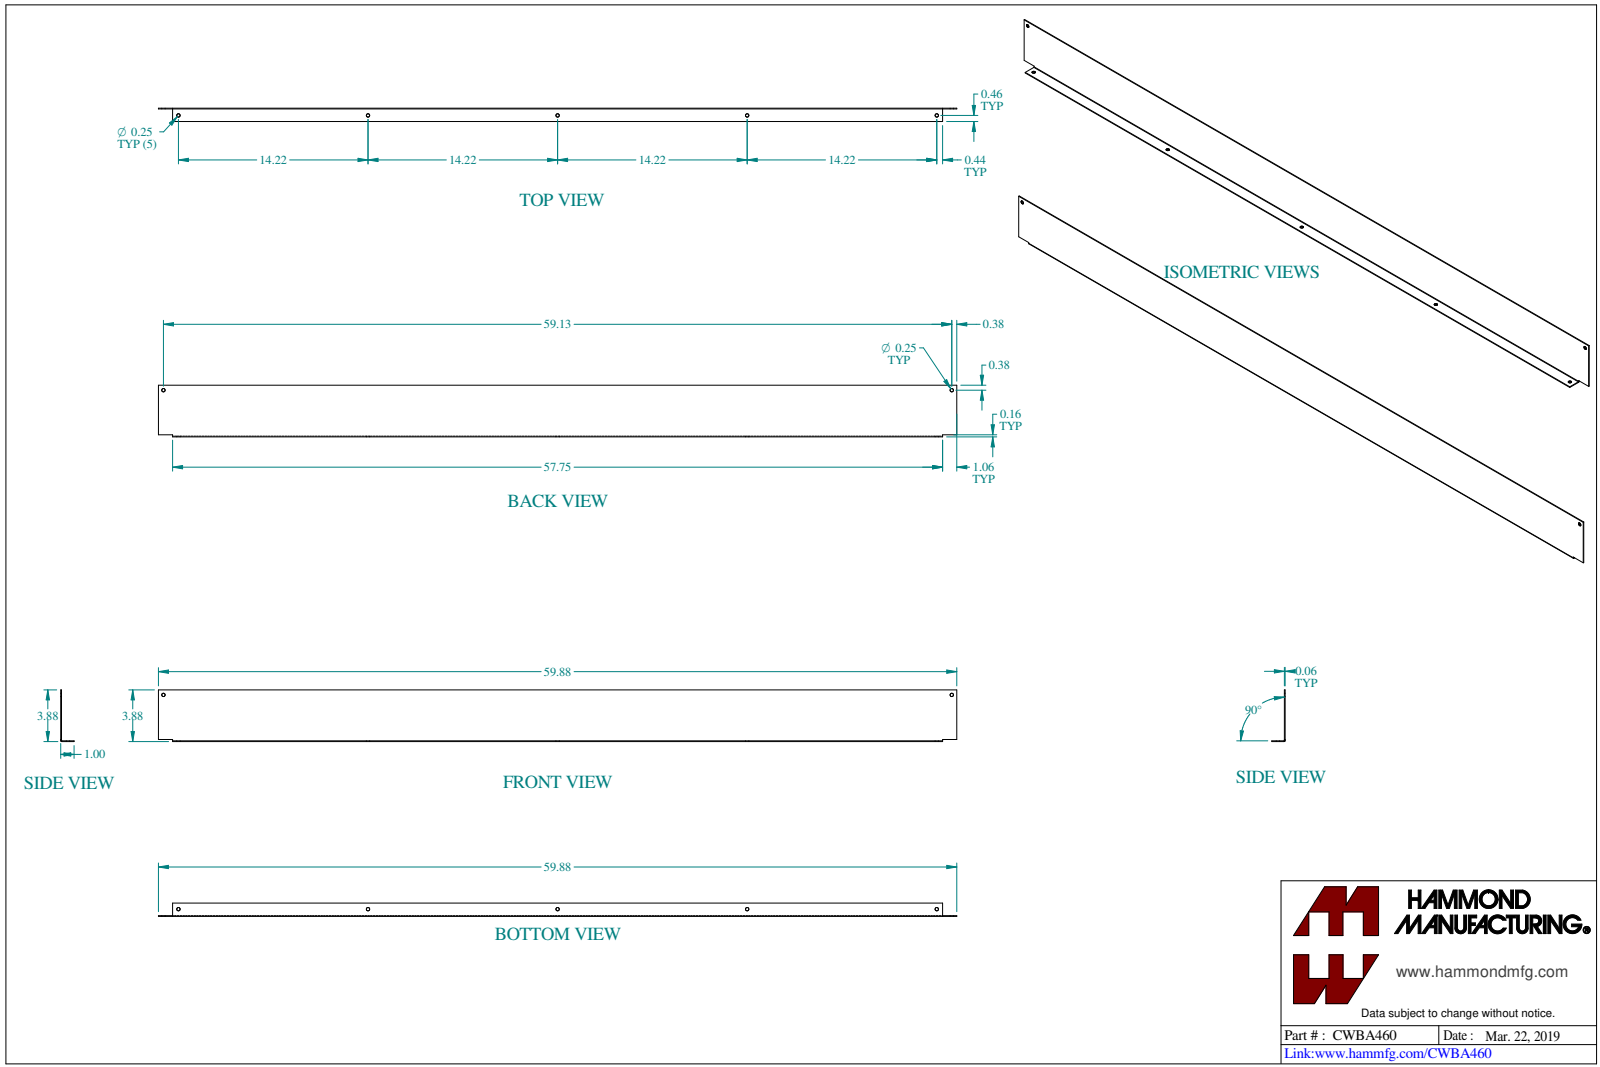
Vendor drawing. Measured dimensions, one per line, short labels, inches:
name: CWBA460
written by: SolidWorks 2023 (CONFIG_CONTROL_DESIGN)
unit: in
bodies: 3 solids, 63 faces (35 planar, 22 cylindrical, 6 other)
size: 59.875 × 4.318 × 1
volume: 16.24 in³; area: 577.5 in²
holes: 7× ⌀0.25, 1× ⌀0.156
bosses: 1× ⌀0.367, 1× ⌀0.19
rounds: 1× R0.029, 1× R0.086
face distances: 0.057, 3.875, 3.818, 1, 0.943, 59.875, 1.063, 58.812, 0.156, 0.099
hole spacings: 14.219, 14.219, 28.437, 42.656, 28.438, 56.875, 59.125
